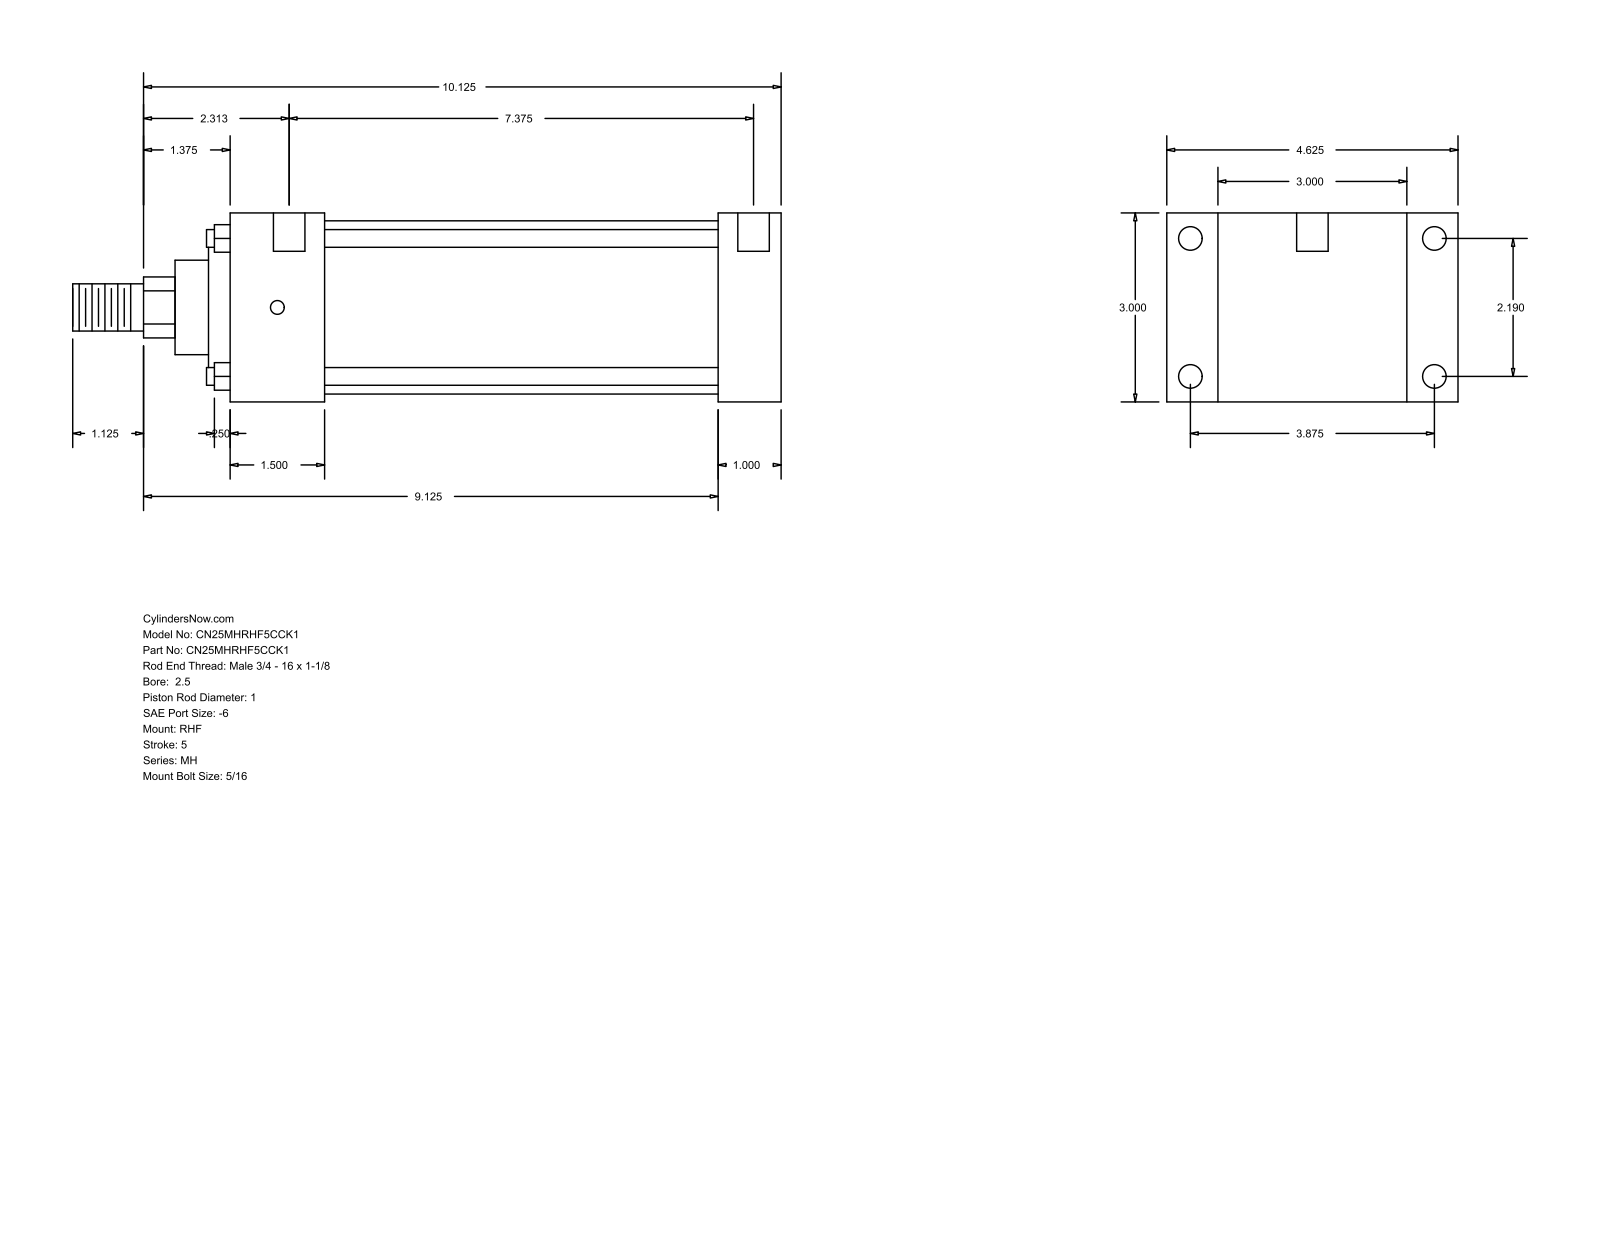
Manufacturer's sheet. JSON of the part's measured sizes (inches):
{"part_name": "MH_RHF__0250_1", "step_written_by": "GSSL Pune (CONFIG_CONTROL_DESIGN)", "units": "inches", "bodies": {"solids": 0, "faces": 90, "planar": 61, "cylindrical": 29, "other": 0}, "overall_size": [11.25, 4.625, 3], "round_holes": [[0.219, 4], [0.375, 4], [0.5, 2]], "round_bosses_or_shafts": [[0.281, 4], [2.75, 1], [2.375, 1], [1.5, 1], [1, 1], [0.75, 1]], "partial_cylinders_radius": [[0.484, 1]], "face_to_face_distances": [3, 1, 0.813, 3.813, 7.75, 8.75, 4.625, 1.5, 6.25, 7.25], "hole_center_spacings": [2.19, 3.875, 4.451, 7.687, 0.125, 0.187, 7.375, 7.5]}
